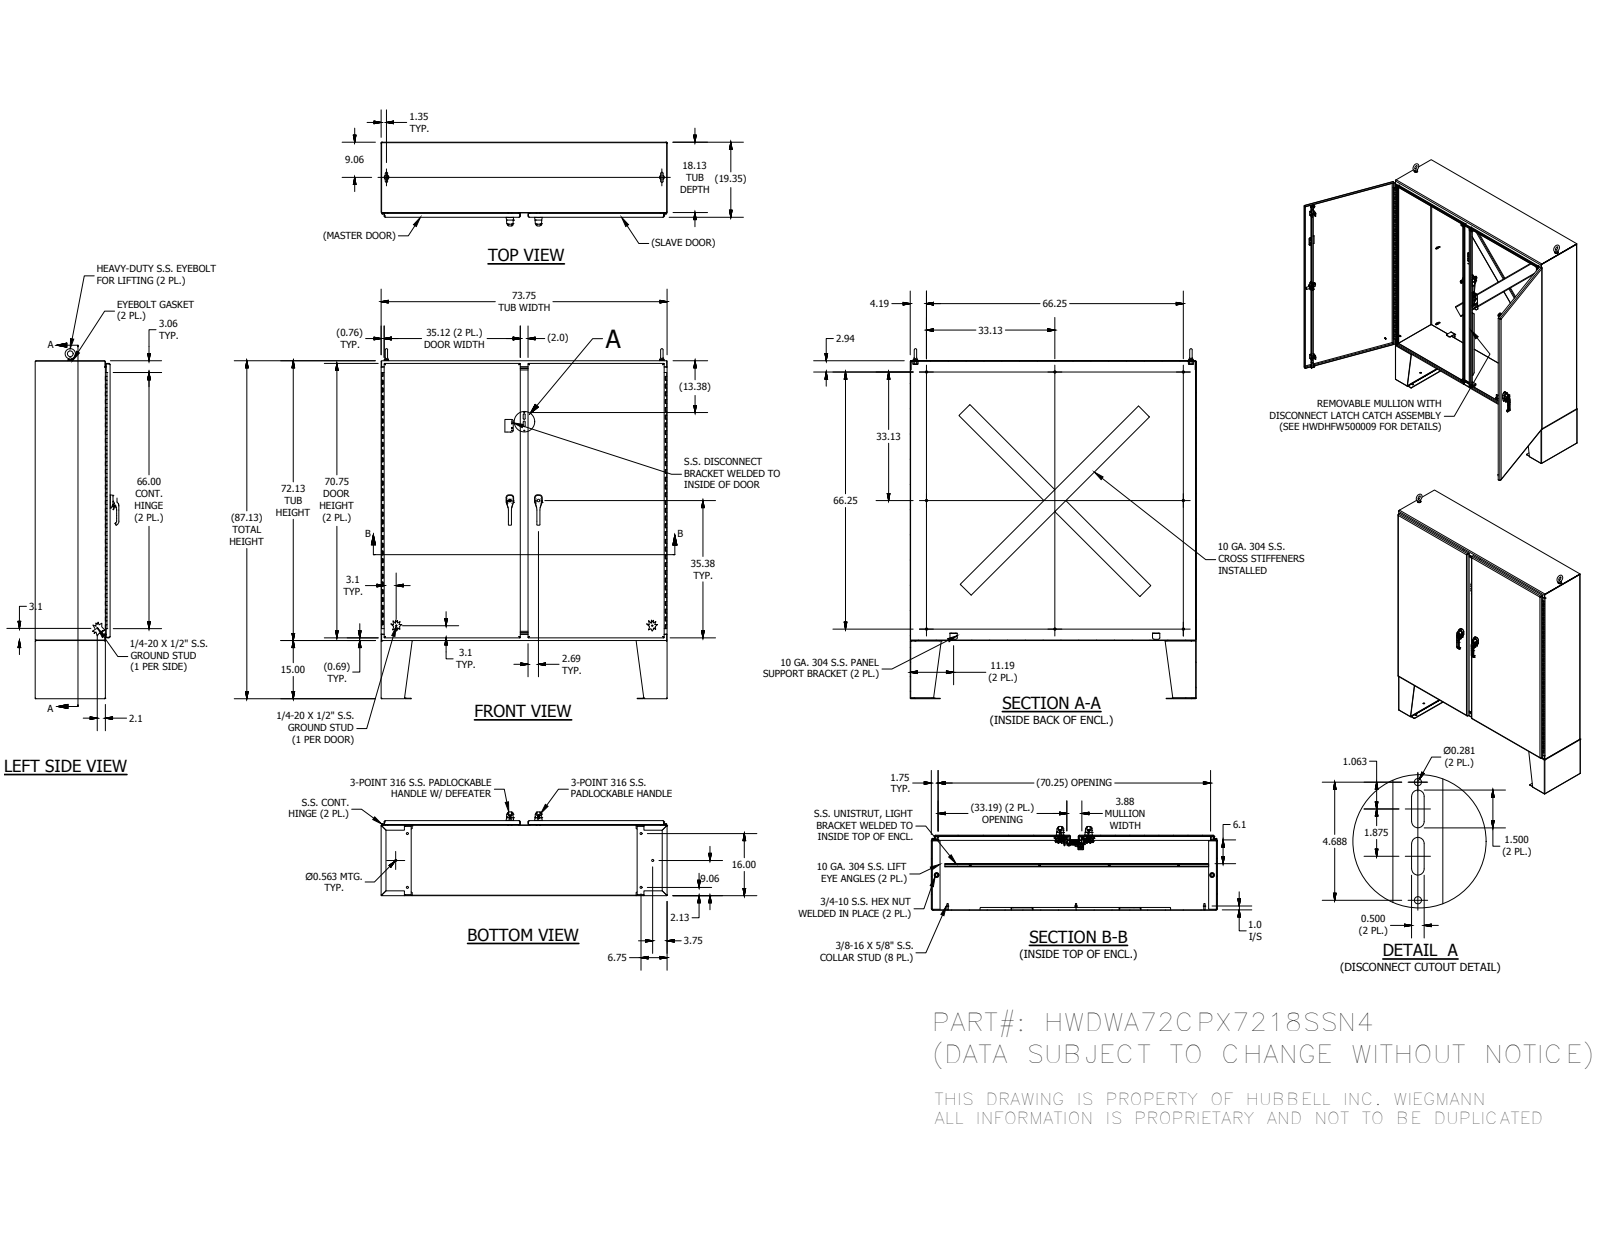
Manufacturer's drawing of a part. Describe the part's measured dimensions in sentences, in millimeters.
The part is named "WA72CPX7218SSN4BLR; WACPX7218SSN4TOP; WACPX7218SSN4BTM; HFW303115 (+8 more)". Its 3-D file was written by "Autodesk Inventor 2016 (AUTOMOTIVE_DESIGN)". It is 215 solids with 8964 faces: 4203 planar, 3005 cylindrical and 1756 other. Overall it measures 2292.29 by 1873.25 by 548.55 millimeters. Its volume is 35 130 000 cubic millimeters and its surface area 26 590 000 square millimeters. Round holes: 20 of diameter 6.35, 18 of diameter 9.52, 18 of diameter 14.29, 12 of diameter 4.98, 10 of diameter 7.14, 9 of diameter 4.76, 8 of diameter 6.65, 6 of diameter 3.96, 6 of diameter 4.83, 6 of diameter 5.4, 6 of diameter 7.33, 6 of diameter 7.37. Round bosses or shafts: 17 of diameter 6.35, 16 of diameter 8.38, 14 of diameter 15.88, 9 of diameter 14.29, 9 of diameter 9.52, 9 of diameter 8.56, 6 of diameter 25.4, 6 of diameter 12.7. Partial cylindrical surfaces (rounded edges, fillets, slot ends): 358 of radius 0.5, 222 of radius 0.3, 144 of radius 0.51, 58 of radius 3.17, 42 of radius 0.47, 28 of radius 1.27, 28 of radius 2, 24 of radius 3.57. The main face-to-face distances are 2.64, 488.79, 486.15, 491.43, 1829.34, 1870.6, 1826.7, 1831.98, 1867.96, 1873.24. The hole center spacings are 9.65, 19.31, 22.5, 30.36, 31.38, 88.97, 127, 173.87.
